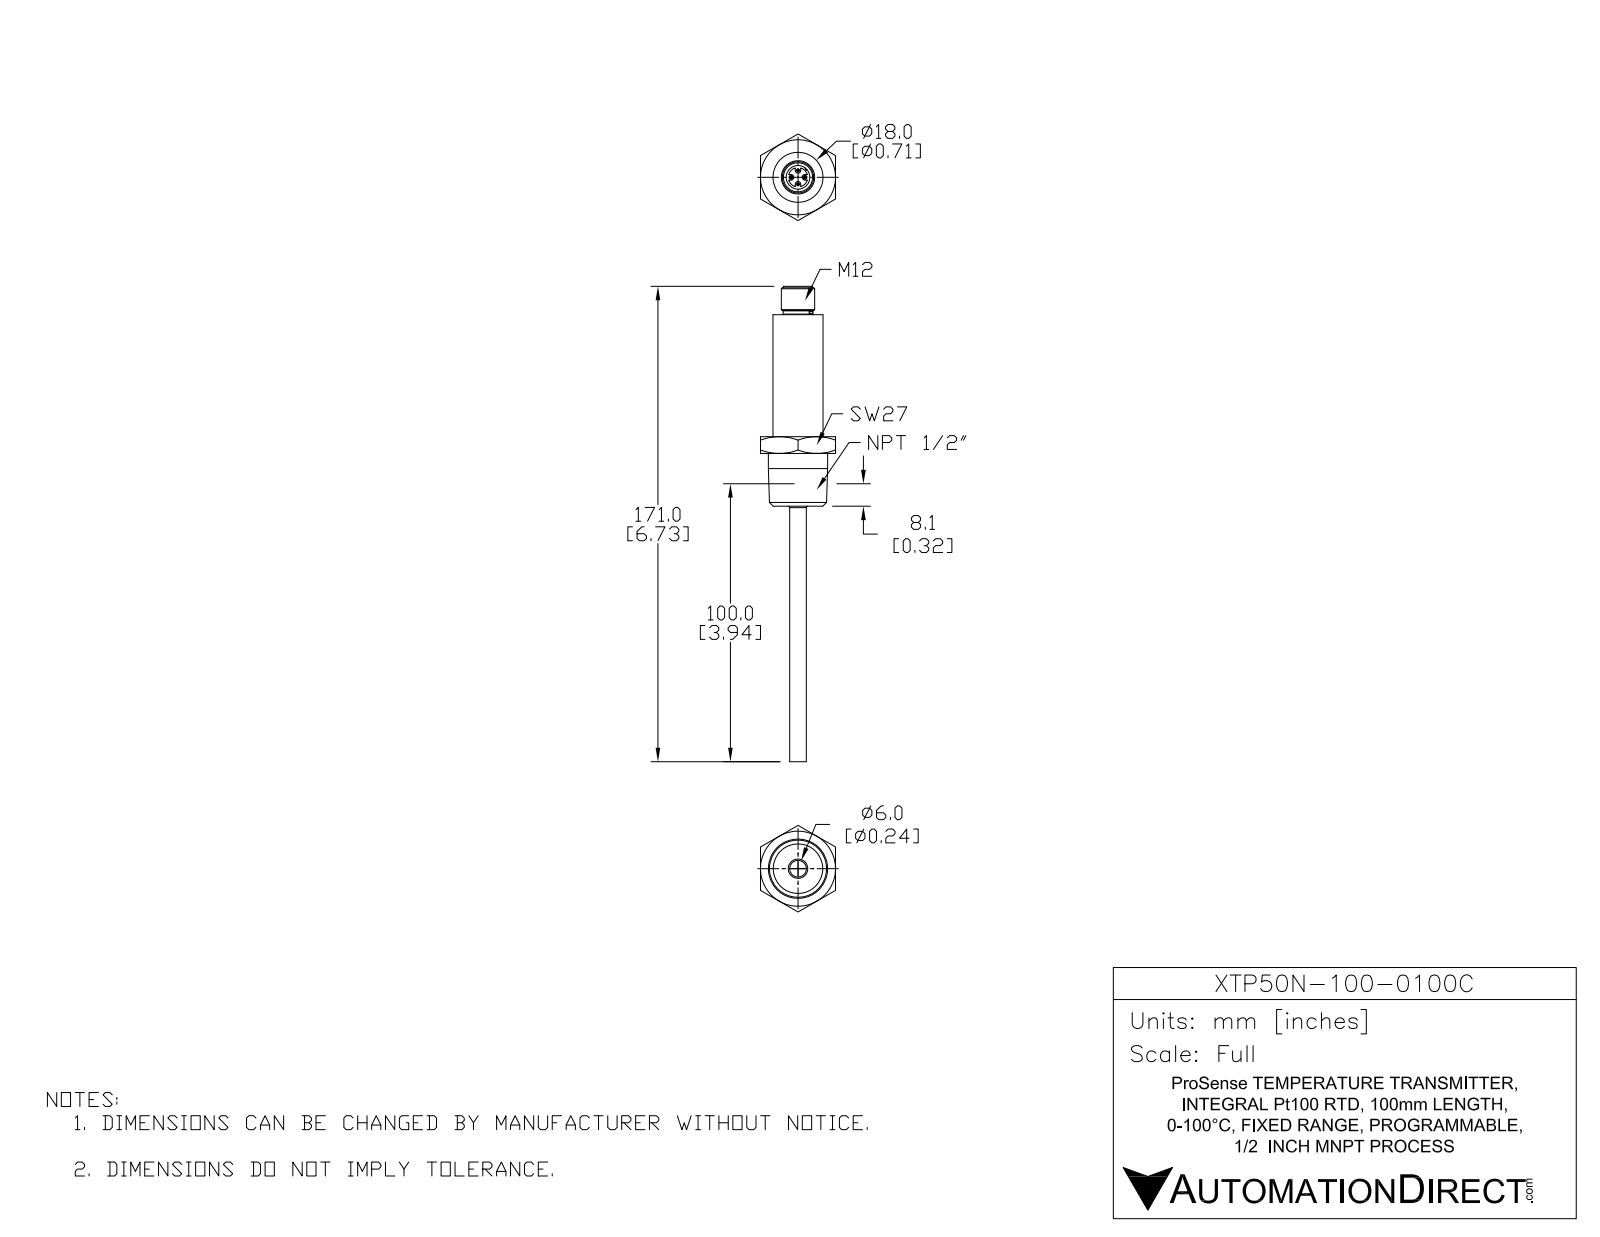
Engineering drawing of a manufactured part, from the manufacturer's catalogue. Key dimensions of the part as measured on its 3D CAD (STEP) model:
Part name (STEP PRODUCT): XTP50N-100-0100C
STEP written by: SolidWorks 2015 (AUTOMOTIVE_DESIGN)
Units: millimetres
Bodies: 1 solid, 117 faces (43 planar, 34 cylindrical, 40 other)
Overall size (bounding box): 171 × 31.18 × 27
Volume: 24 334 mm³ · Surface area: 8 216 mm²
Round holes (diameter × count): ⌀4 ×1, ⌀8.5 ×1
Round bosses / shafts (diameter × count): ⌀1.02 ×4, ⌀21.34 ×1, ⌀18 ×1, ⌀12 ×1, ⌀10.7 ×1, ⌀10.5 ×1, ⌀6 ×1
Partial cylindrical surfaces — rounded edges, fillets, slot ends (radius × count): R1 ×4, R3.5 ×1, R4.25 ×1
Main face-to-face distances: 27, 25, 19, 6, 68.9, 49.9, 43.9, 79.1, 60.1, 54.1
